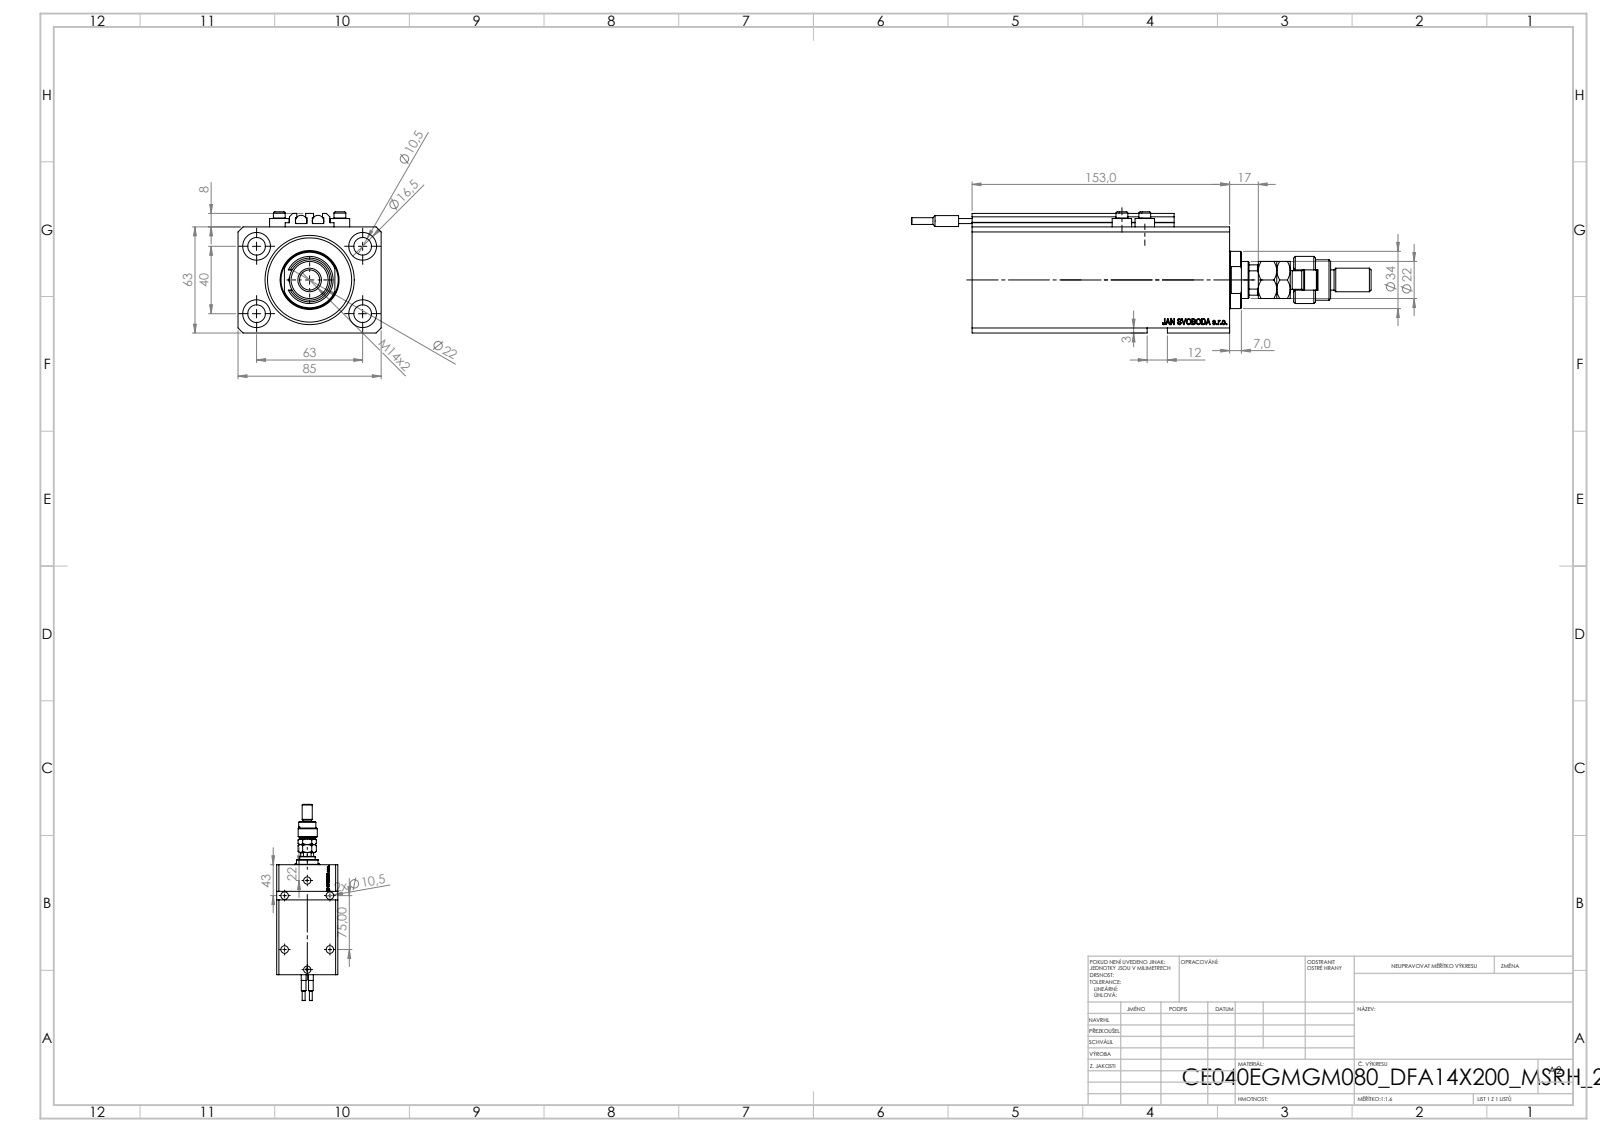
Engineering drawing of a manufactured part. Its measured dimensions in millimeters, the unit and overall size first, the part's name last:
Units: millimetres
Overall size (bounding box): 273 × 85 × 72
Round holes (diameter × count): ⌀10.5 ×8, ⌀1.25 ×4, ⌀4 ×4, ⌀16.5 ×4, ⌀10 ×2, ⌀13.16 ×2, ⌀20 ×2, ⌀12.5 ×1, ⌀22 ×1, ⌀40 ×1, ⌀53 ×1
Round bosses / shafts (diameter × count): ⌀11.6 ×4, ⌀7 ×4, ⌀6.8 ×2, ⌀6.5 ×2, ⌀4 ×2, ⌀34 ×1, ⌀28 ×1, ⌀24 ×1
Partial cylindrical surfaces — rounded edges, fillets, slot ends (radius × count): R0.2 ×10, R9.75 ×1, R10.5 ×1
Main face-to-face distances: 63, 85, 17, 153, 136, 3, 65, 11.4, 124.6, 141.6
Hole centre spacings: 37.31, 63, 13.6, 15.4, 24.96, 33.62, 36, 37.86
Volume: 709 336 mm³ · Surface area: 151 534 mm²
Bodies: 12 solids, 1244 faces (595 planar, 171 cylindrical, 478 other)
Part name (STEP PRODUCT): MFA; V250CE_VC_E; V250CE_E_Body; V250CE_C_VCP (+3 more)
STEP written by: SolidWorks 2019 (CONFIG_CONTROL_DESIGN)
